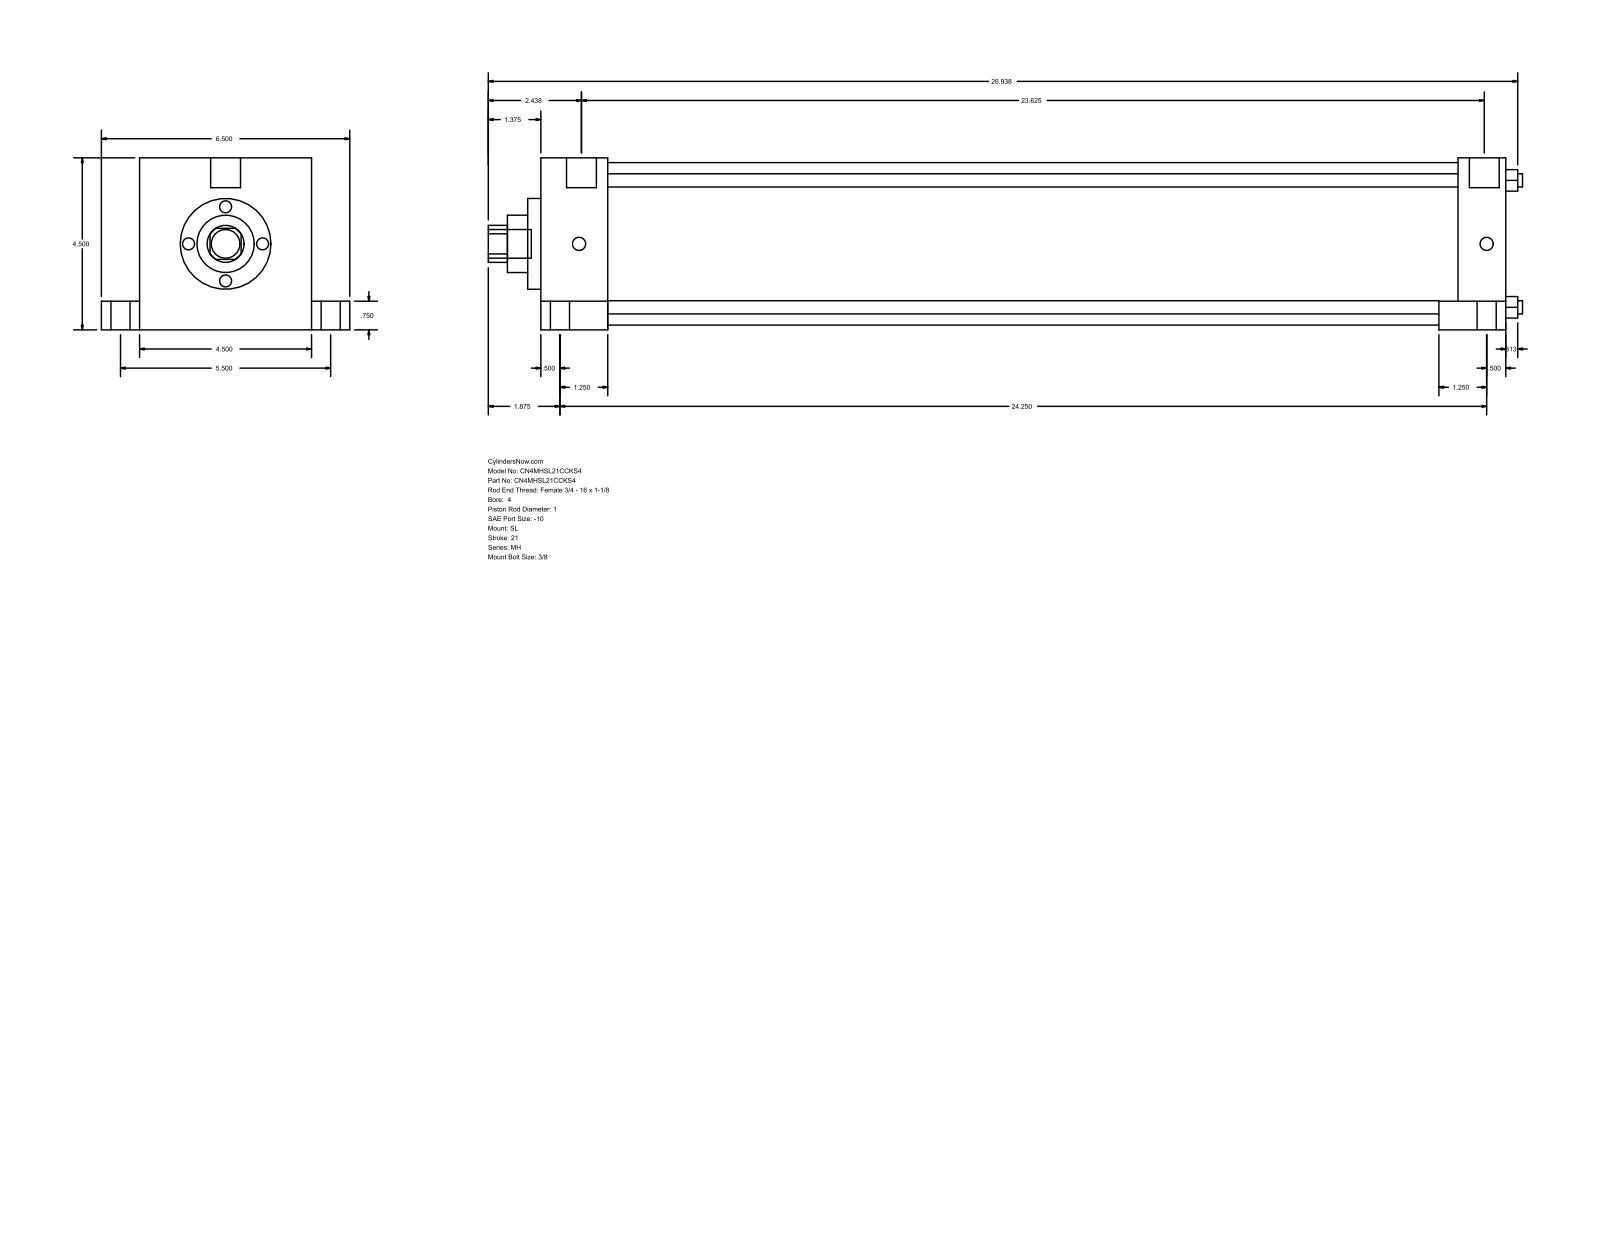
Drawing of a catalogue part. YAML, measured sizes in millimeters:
part_name: "MH_SL__0400_1"
step_written_by: "GSSL Pune (CONFIG_CONTROL_DESIGN)"
units: millimeters
bodies: {solids: 0, faces: 110, planar: 77, cylindrical: 33, other: 0}
overall_size: [687.39, 165.1, 114.3]
round_holes:
  - {diameter: 8.76, count: 4}
  - {diameter: 25.4, count: 1}
  - {diameter: 38.1, count: 1}
  - {diameter: 60.33, count: 1}
  - {diameter: 107.95, count: 1}
round_bosses_or_shafts:
  - {diameter: 19.05, count: 5}
  - {diameter: 12.7, count: 4}
  - {diameter: 8.73, count: 4}
  - {diameter: 19.84, count: 2}
partial_cylinders:
  - {radius: 12.29, count: 1}
face_to_face_distances: [114.3, 641.35, 44.46, 596.89, 609.6, 565.14, 31.75, 25.4, 139.7, 19.05]
hole_center_spacings: [59.62, 84.32, 119.25]
